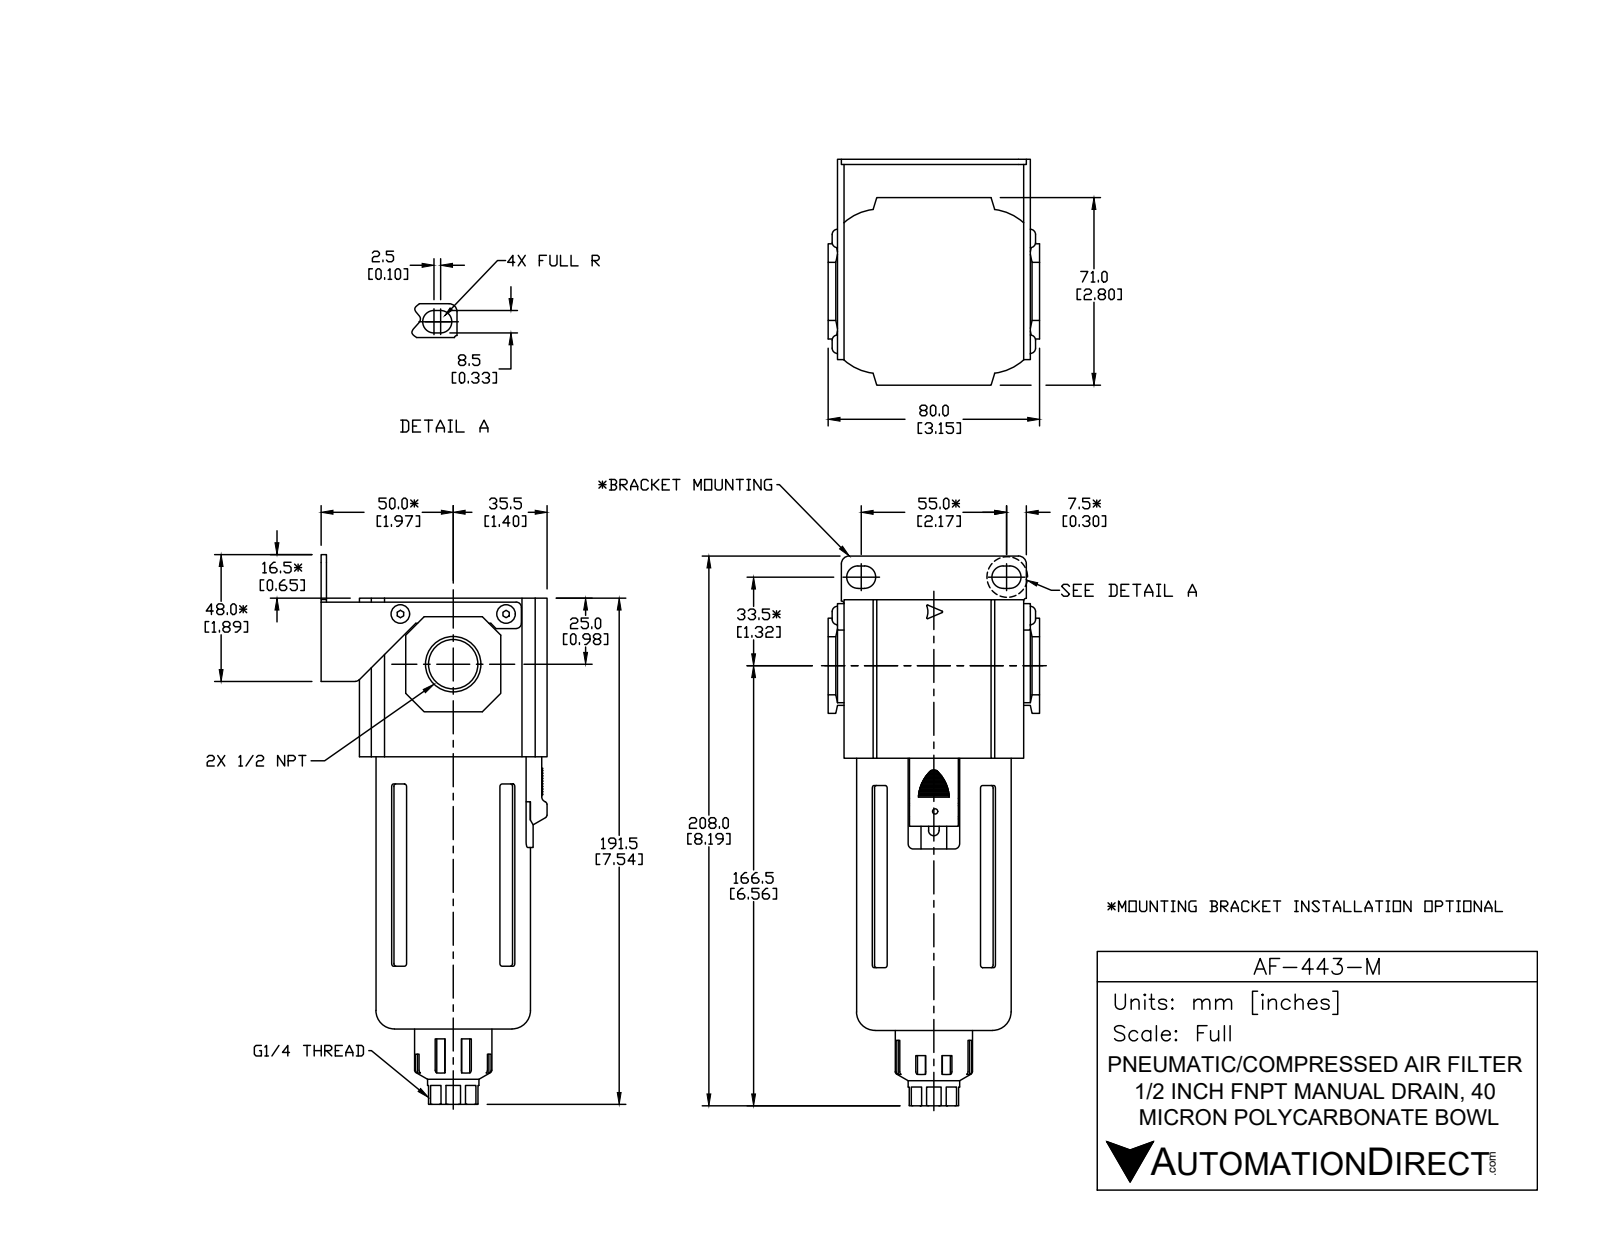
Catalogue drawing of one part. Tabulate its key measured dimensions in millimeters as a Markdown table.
| quantity | value |
| --- | --- |
| part name | AF-443-M |
| STEP written by | SolidWorks 2015 (CONFIG_CONTROL_DESIGN) |
| units | millimeters |
| bodies | 9 solids, 394 faces (246 planar, 94 cylindrical, 54 other) |
| overall size | 208 × 85.5 × 80 |
| volume | 389 619 mm³ |
| surface area | 93 830 mm² |
| round holes (diameter × count) | 3.4 × 2, 8.57 × 1, 17.86 × 1, 50 × 1, 59.72 × 1 |
| round bosses / shafts (diameter × count) | 58.48 × 1, 33.4 × 1, 29.24 × 1, 19.49 × 1 |
| partial cylindrical surfaces (radius × count) | 1 × 18, 2 × 8, 9.5 × 8, 0.5 × 6, 0.3 × 4, 4.25 × 4, 20 × 4, 0.2 × 3 |
| main face-to-face distances | 2.5, 68, 70.5, 83, 85.5, 14.5, 12, 71, 163, 109.7 |
| hole center spacings | 27.59, 40 |
